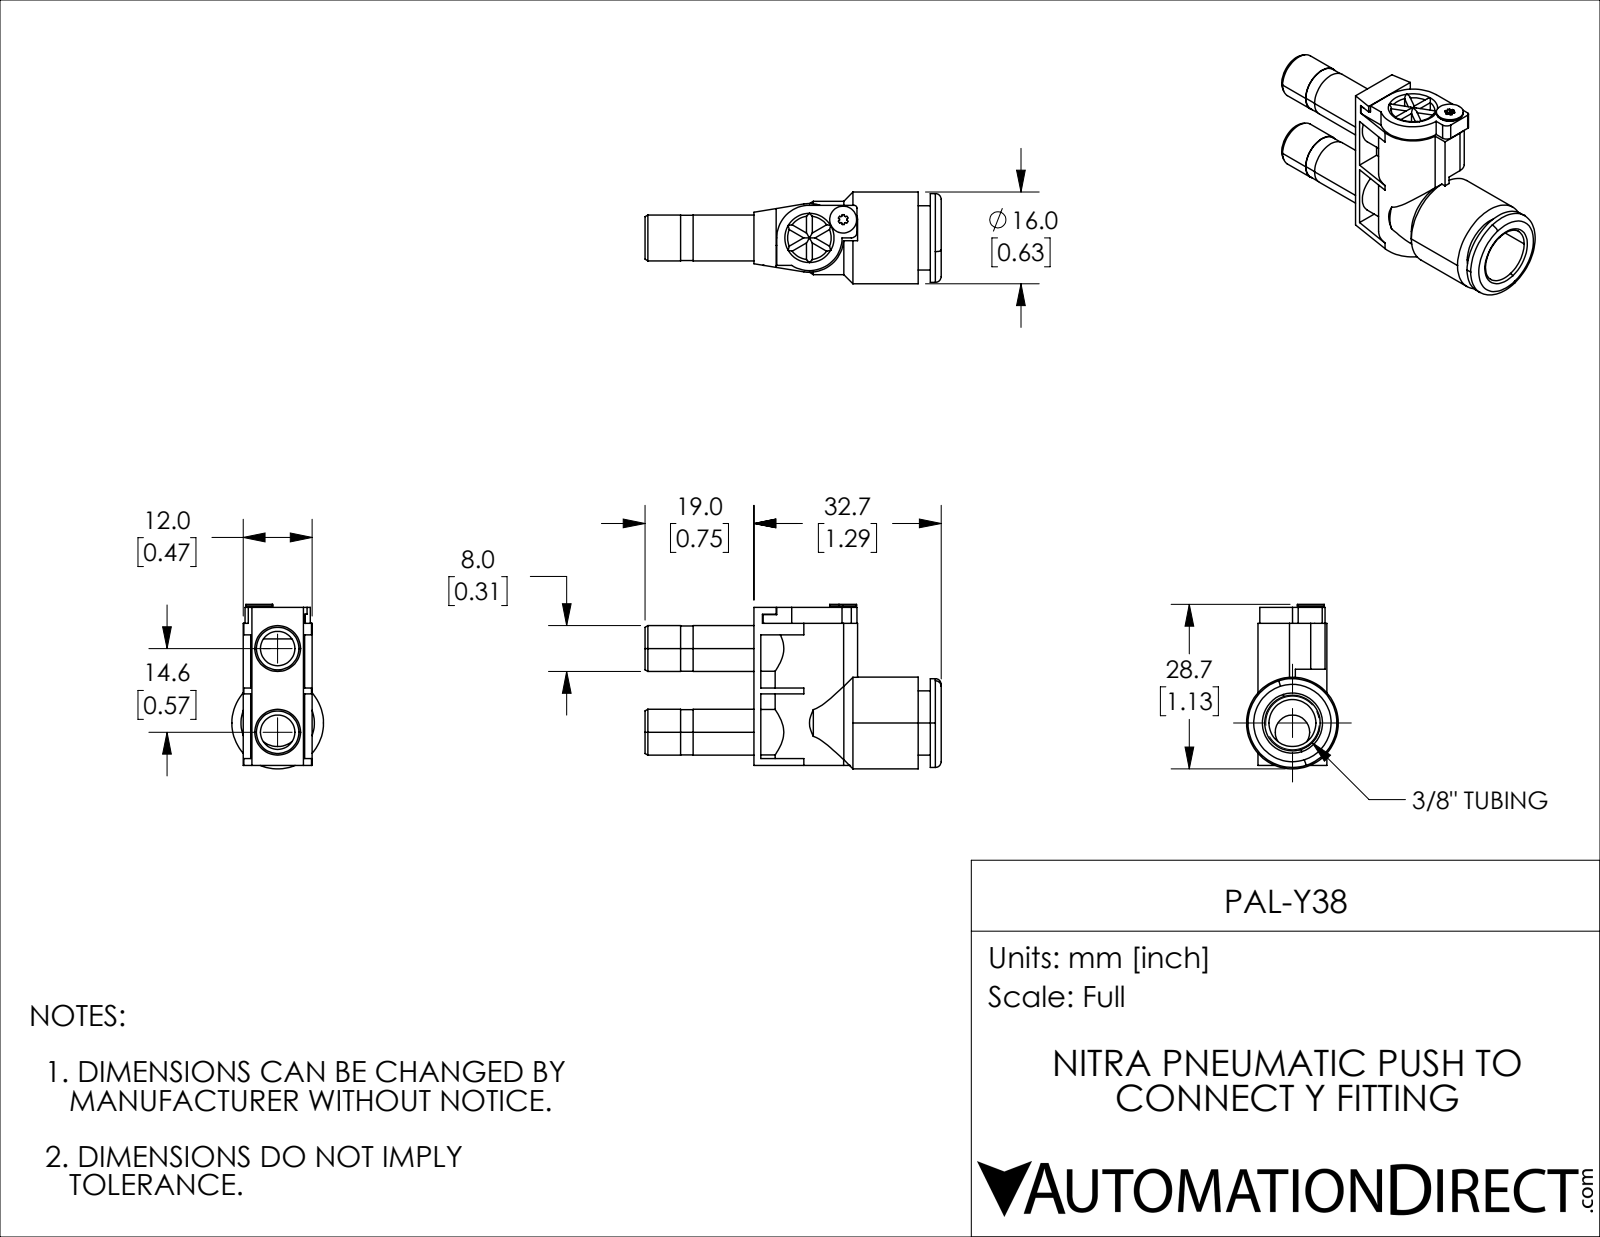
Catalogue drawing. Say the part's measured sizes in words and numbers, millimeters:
The part is named "PAL-Y38". Its 3-D file was written by "SolidWorks 2019 (CONFIG_CONTROL_DESIGN)". It is 1 solid with 178 faces: 92 planar, 67 cylindrical and 19 other. Overall it measures 51.7 by 28.7 by 16 millimeters. Its volume is 5 249 cubic millimeters and its surface area 6 308 square millimeters. Round holes: 2 of diameter 6, 1 of diameter 8.2, 1 of diameter 8.4, 1 of diameter 9.7. Round bosses or shafts: 2 of diameter 8, 2 of diameter 7.9, 1 of diameter 16, 1 of diameter 15.5, 1 of diameter 12.8, 1 of diameter 12, 1 of diameter 11.2, 1 of diameter 4.7. Partial cylindrical surfaces (rounded edges, fillets, slot ends): 4 of radius 0.5, 1 of radius 0.65, 1 of radius 0.88, 1 of radius 1, 1 of radius 2.5, 1 of radius 3.8, 1 of radius 5.7. The main face-to-face distances are 1.2, 28.7, 1, 27.5, 27.6, 30.8, 29.6, 2.1, 0.5, 4. The hole center spacings are 1.6, 13, 14.6.
